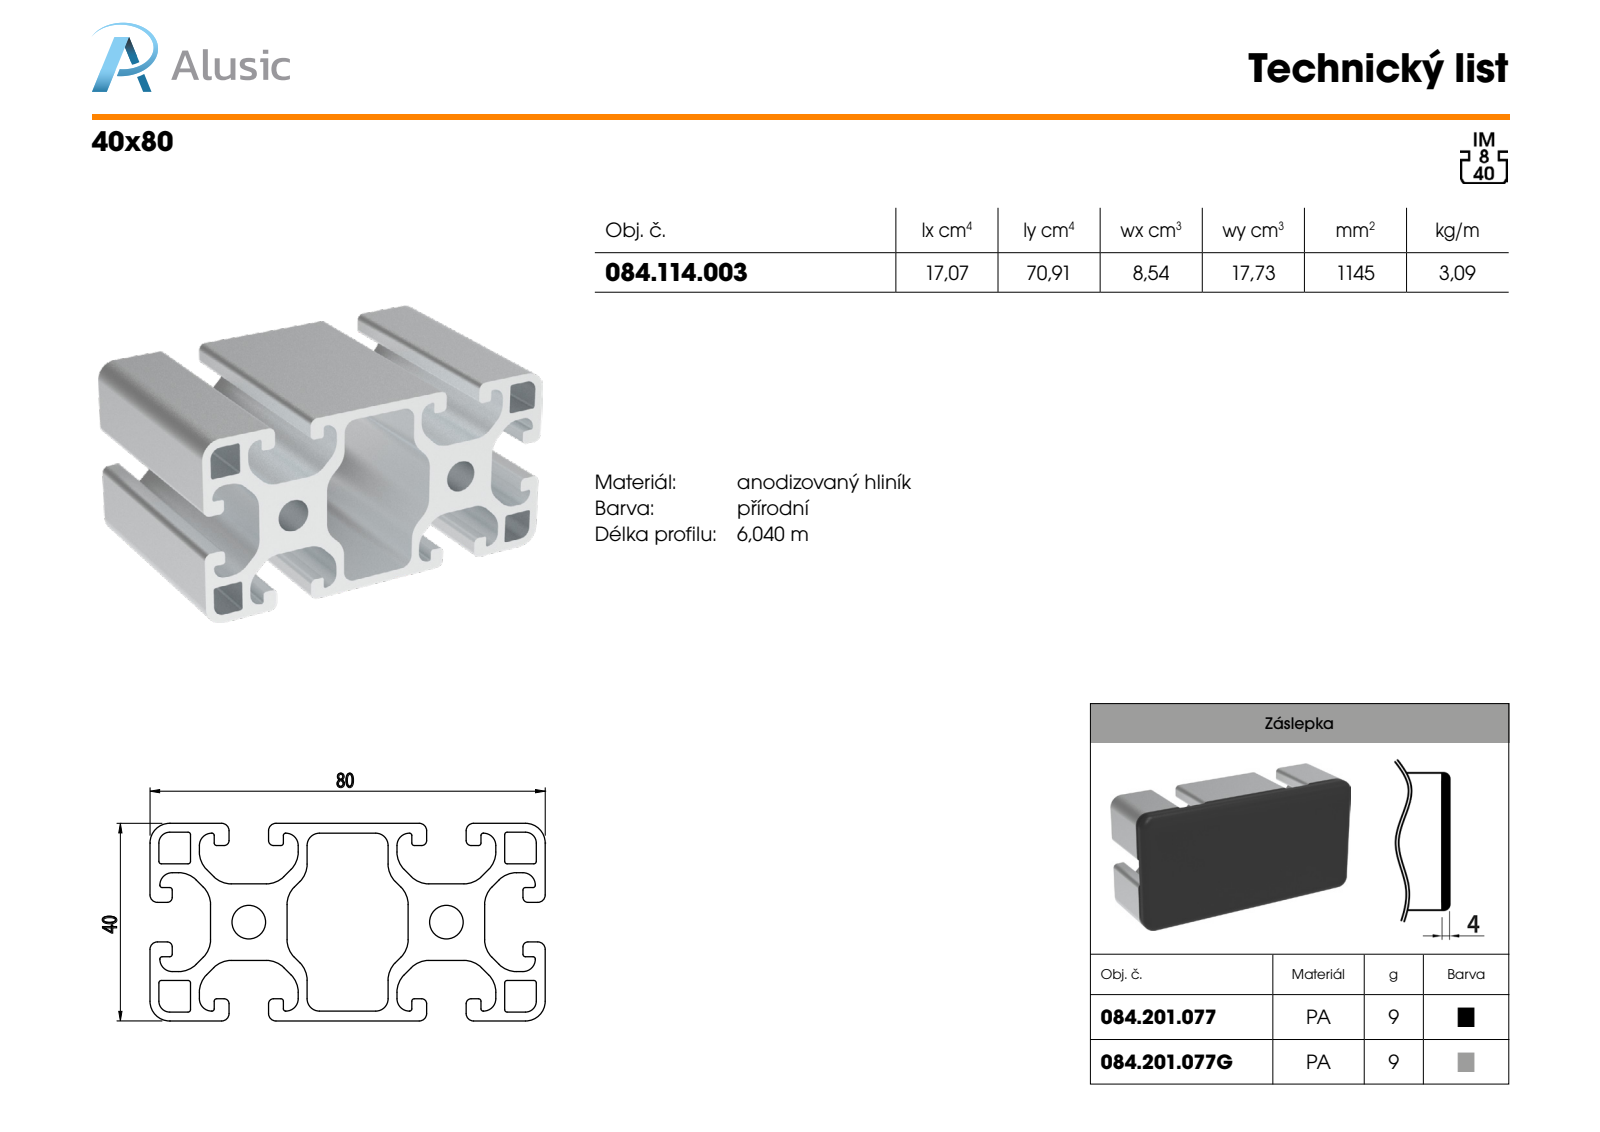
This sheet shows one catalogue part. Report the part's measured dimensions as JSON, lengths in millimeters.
{"part_name": "084.114.003", "step_written_by": "SolidWorks 2018 (AUTOMOTIVE_DESIGN)", "units": "millimeters", "bodies": {"solids": 1, "faces": 238, "planar": 117, "cylindrical": 121, "other": 0}, "overall_size": [100, 80, 40], "volume_mm3": 114473, "surface_area_mm2": 78476, "round_holes": [[6.8, 2]], "partial_cylinders_radius": [[5, 32], [0.5, 24], [2.5, 16], [0.45, 12], [1, 12], [1.5, 12], [2.2, 4], [4, 4]], "face_to_face_distances": [40, 4.05, 19.55, 8.2, 27.75, 12.25, 3, 31.8, 1.8, 30], "hole_center_spacings": [40]}
